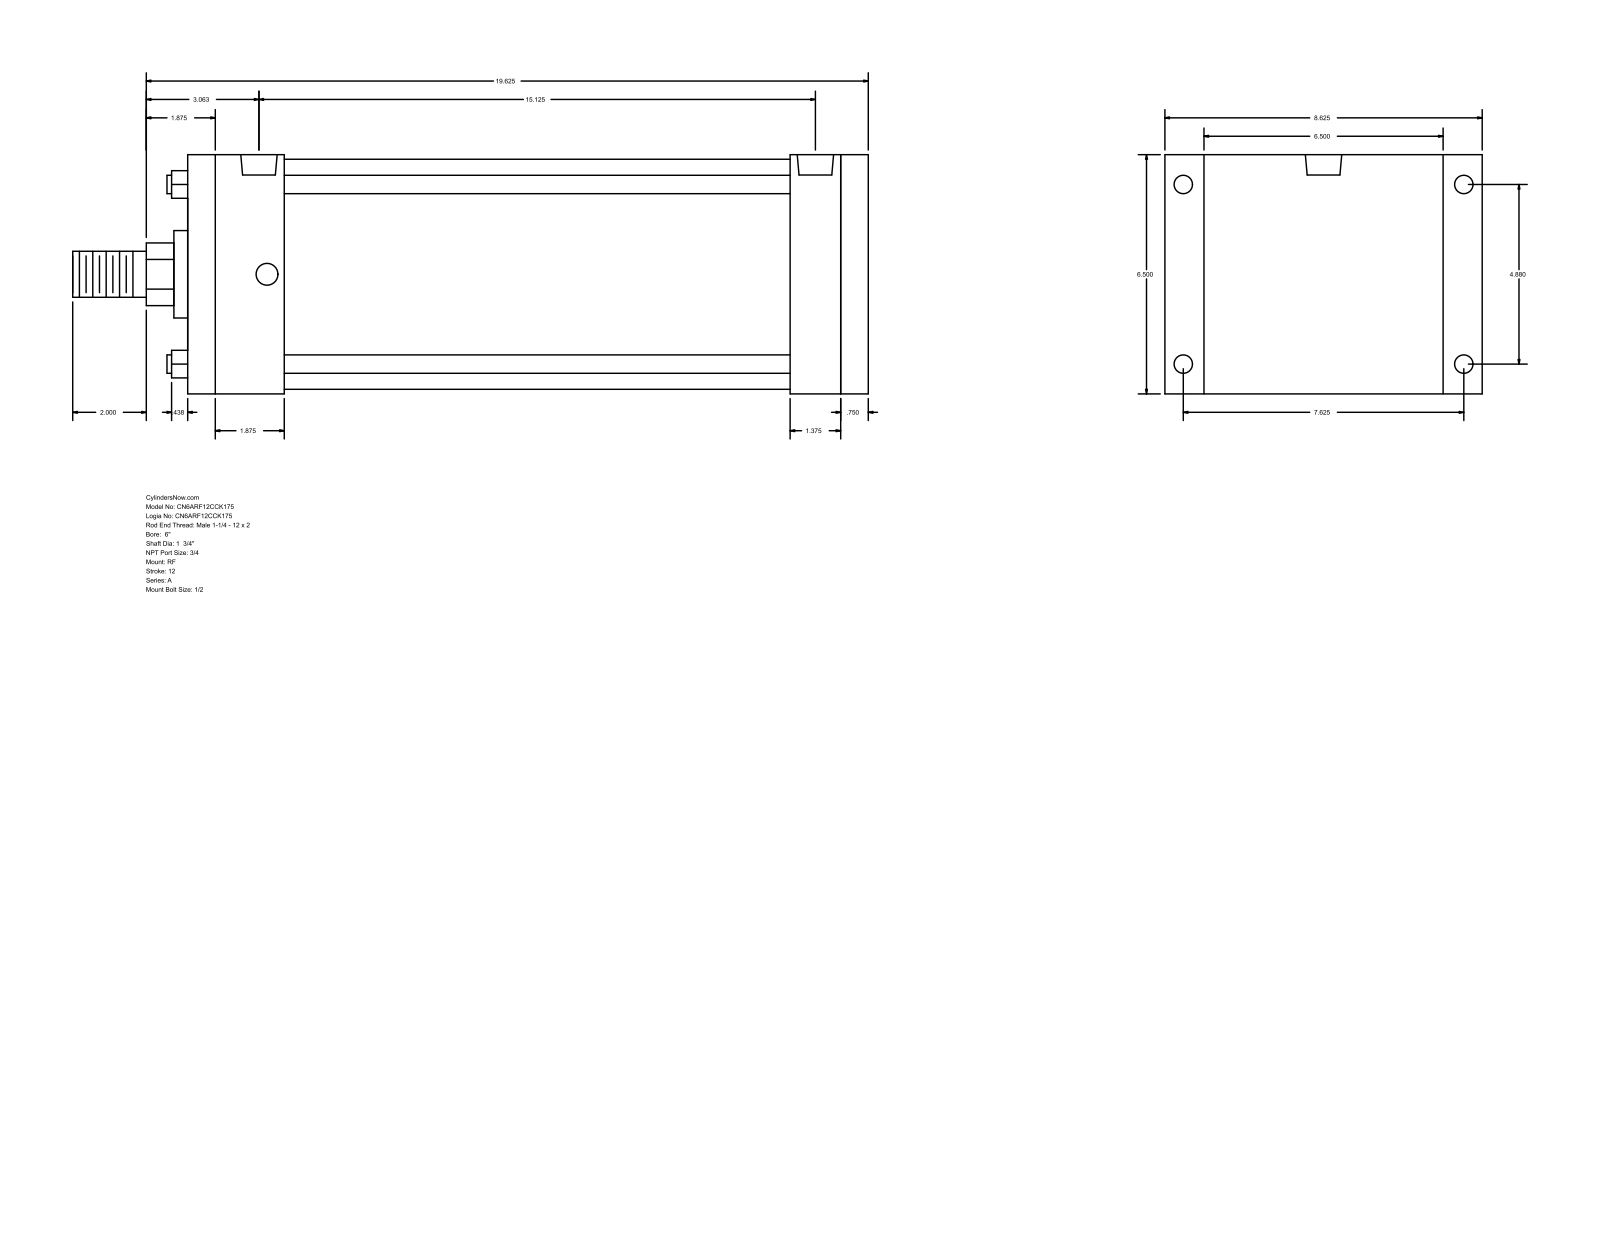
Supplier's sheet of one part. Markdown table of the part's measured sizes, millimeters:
| quantity | value |
| --- | --- |
| part name | A_RF__0600_1.75 |
| STEP written by | GSSL Pune (CONFIG_CONTROL_DESIGN) |
| units | millimeters |
| bodies | 0 solids, 92 faces (64 planar, 28 cylindrical, 0 other) |
| overall size | 549.27 × 219.07 × 165.1 |
| round holes (diameter × count) | 12.7 × 4, 15.08 × 4, 25.12 × 2 |
| round bosses / shafts (diameter × count) | 12.7 × 4, 158.75 × 1, 60.33 × 1, 44.45 × 1, 31.75 × 1 |
| partial cylindrical surfaces (radius × count) | 21.63 × 1 |
| main face-to-face distances | 165.1, 469.91, 19.05, 450.86, 66.68, 384.18, 403.23, 415.93, 349.25, 34.93 |
| hole center spacings | 5.56, 123.96, 193.68, 229.95, 373.05, 378.61, 384.17 |
